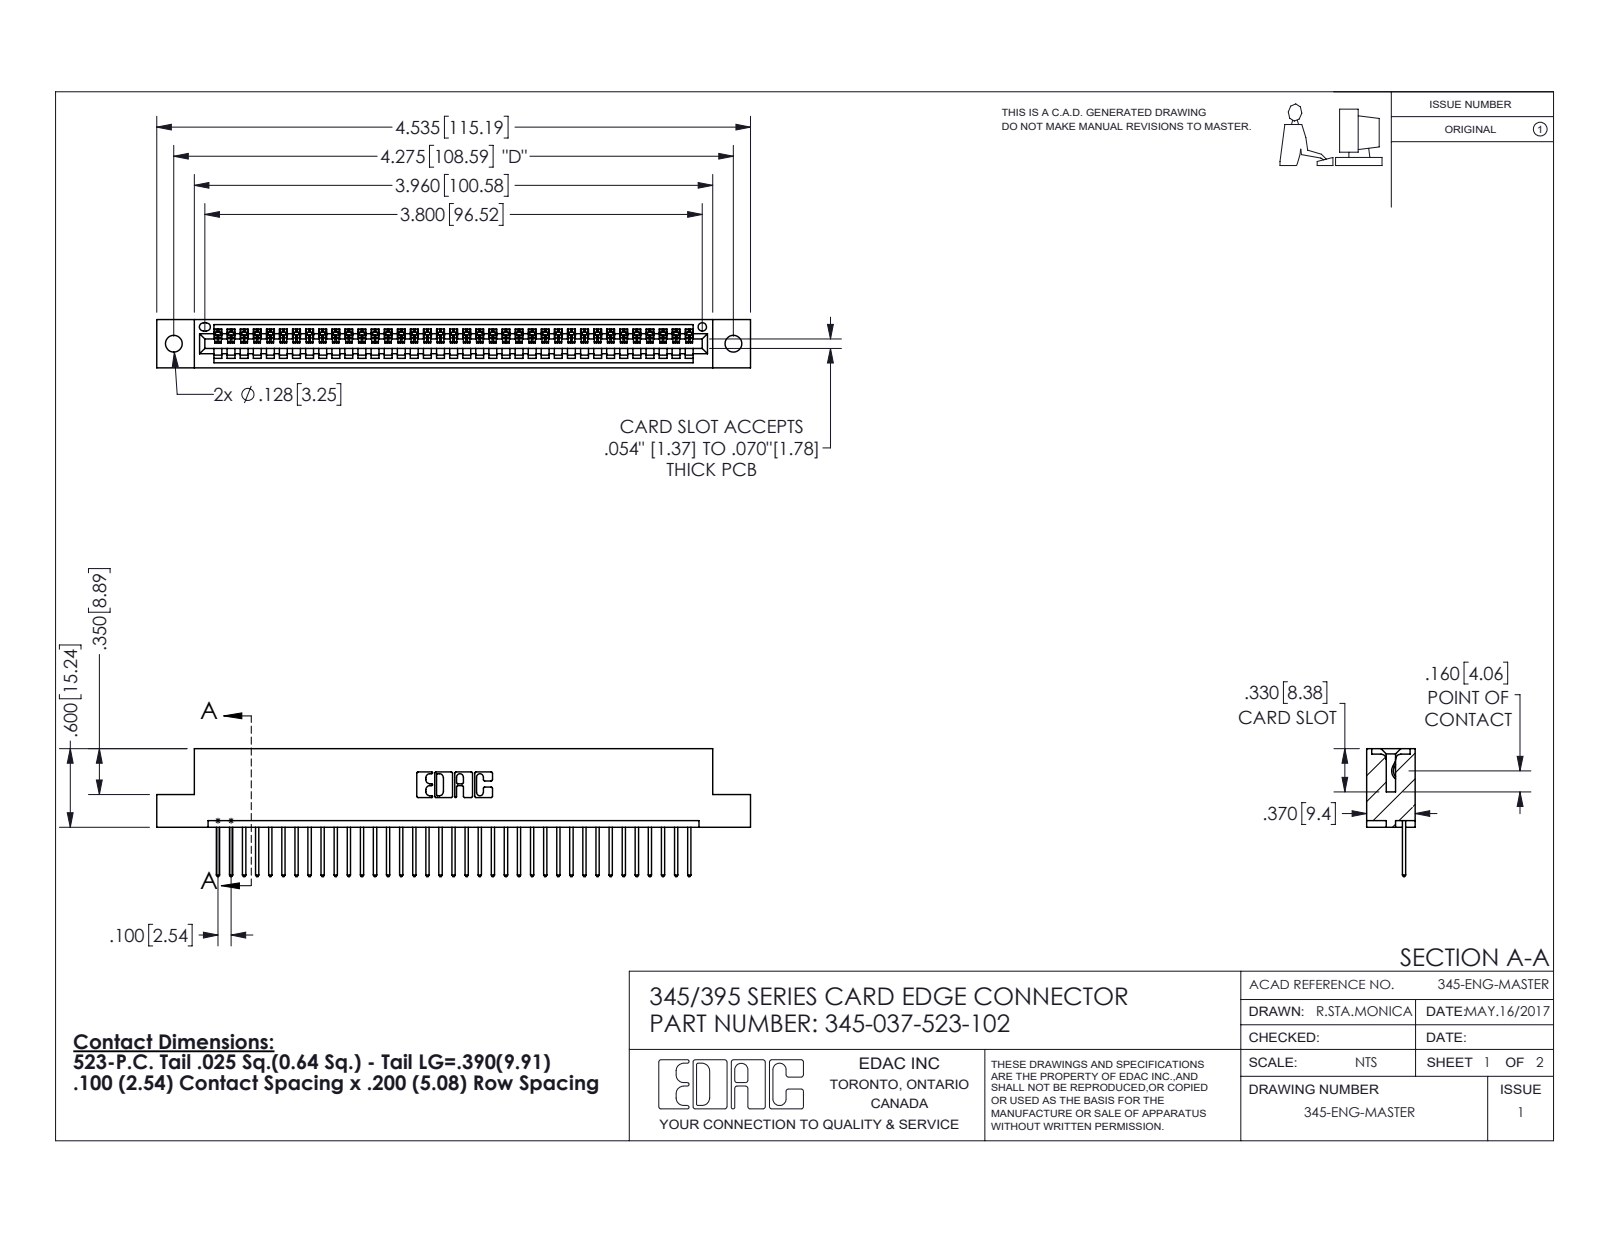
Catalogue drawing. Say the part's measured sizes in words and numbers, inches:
The part is named "345 Part_Flush Mounting Lugs - 0.128 Dia; 345-037-523-102; 345-292-001_345-293-123". Its 3-D file was written by "SolidWorks 2016 (CONFIG_CONTROL_DESIGN)". It is 38 solids with 2272 faces: 1560 planar, 712 cylindrical and 0 other. Overall it measures 4.535 by 0.977 by 0.37 inches. Its volume is 0.662 cubic inches and its surface area 21.88 square inches. Round holes: 2 of diameter 0.128, 1 of diameter 0.064. Partial cylindrical surfaces (rounded edges, fillets, slot ends): 74 of radius 0.006, 74 of radius 0.01, 22 of radius 0.01, 6 of radius 0.007, 6 of radius 0.031, 3 of radius 0.026, 2 of radius 0.031, 2 of radius 0.04. The main face-to-face distances are 0.298, 0.072, 0.2, 0.37, 0.098, 0.272, 0.025, 0.225, 0.149, 0.072. The hole center spacings are 0.27, 4.039, 4.275.
